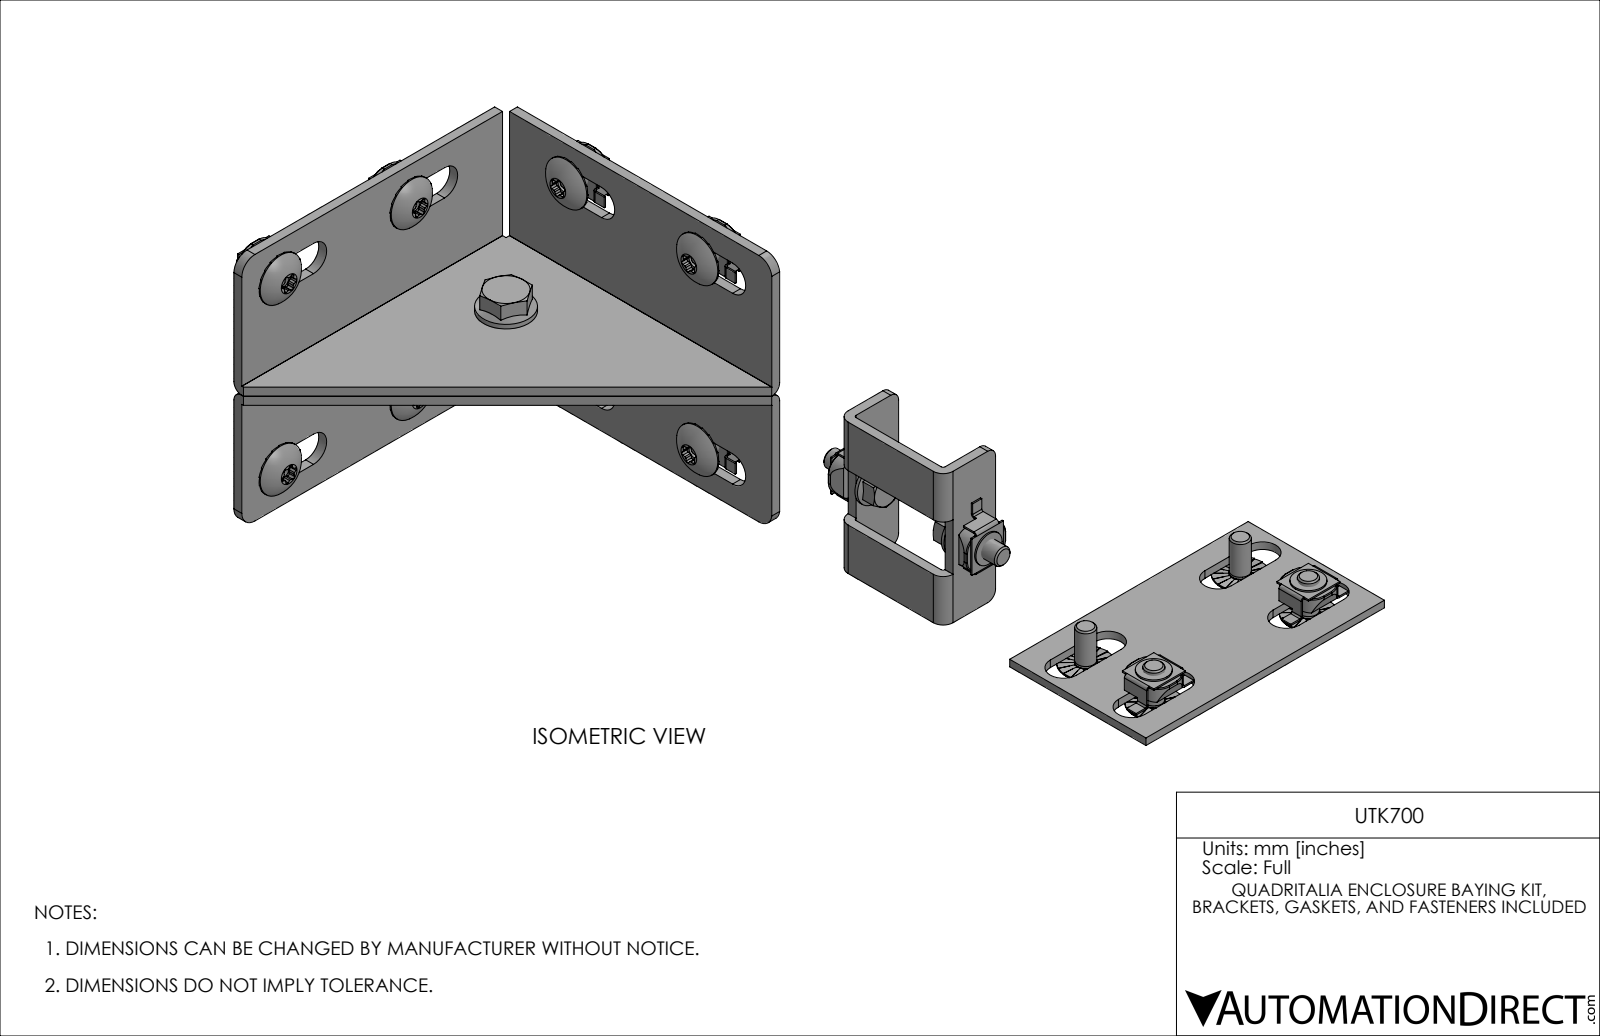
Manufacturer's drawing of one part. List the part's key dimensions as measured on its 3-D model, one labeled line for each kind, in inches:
Part name (STEP PRODUCT): UTK700
STEP written by: SolidWorks 2021 (CONFIG_CONTROL_DESIGN)
Units: inches
Bodies: 32 solids, 2444 faces (1836 planar, 480 cylindrical, 128 other)
Overall size (bounding box): 10.088 × 7.553 × 3.61
Volume: 7.149 in³ · Surface area: 146.8 in²
Round holes (diameter × count): ⌀0.154 ×12, ⌀0.194 ×11, ⌀0.323 ×11, ⌀0.394 ×8, ⌀0.194 ×1, ⌀0.315 ×1, ⌀0.472 ×1
Round bosses / shafts (diameter × count): ⌀0.236 ×13, ⌀0.618 ×12, ⌀0.315 ×11, ⌀0.394 ×3, ⌀0.669 ×1, ⌀0.528 ×1, ⌀0.512 ×1
Partial cylindrical surfaces — rounded edges, fillets, slot ends (radius × count): R0.02 ×176, R0.177 ×44, R0.039 ×32, R0.01 ×30, R0.197 ×20, R0.118 ×4, R0.03 ×2, R0.118 ×2
Main face-to-face distances: 0.118, 0.236, 1.732, 1.614, 1.85, 0.098, 1.516, 1.634, 1.752, 0.197
Hole centre spacings: 1.969, 2.48, 3.167, 1.024, 2.323, 2.538, 1.894, 2.702
